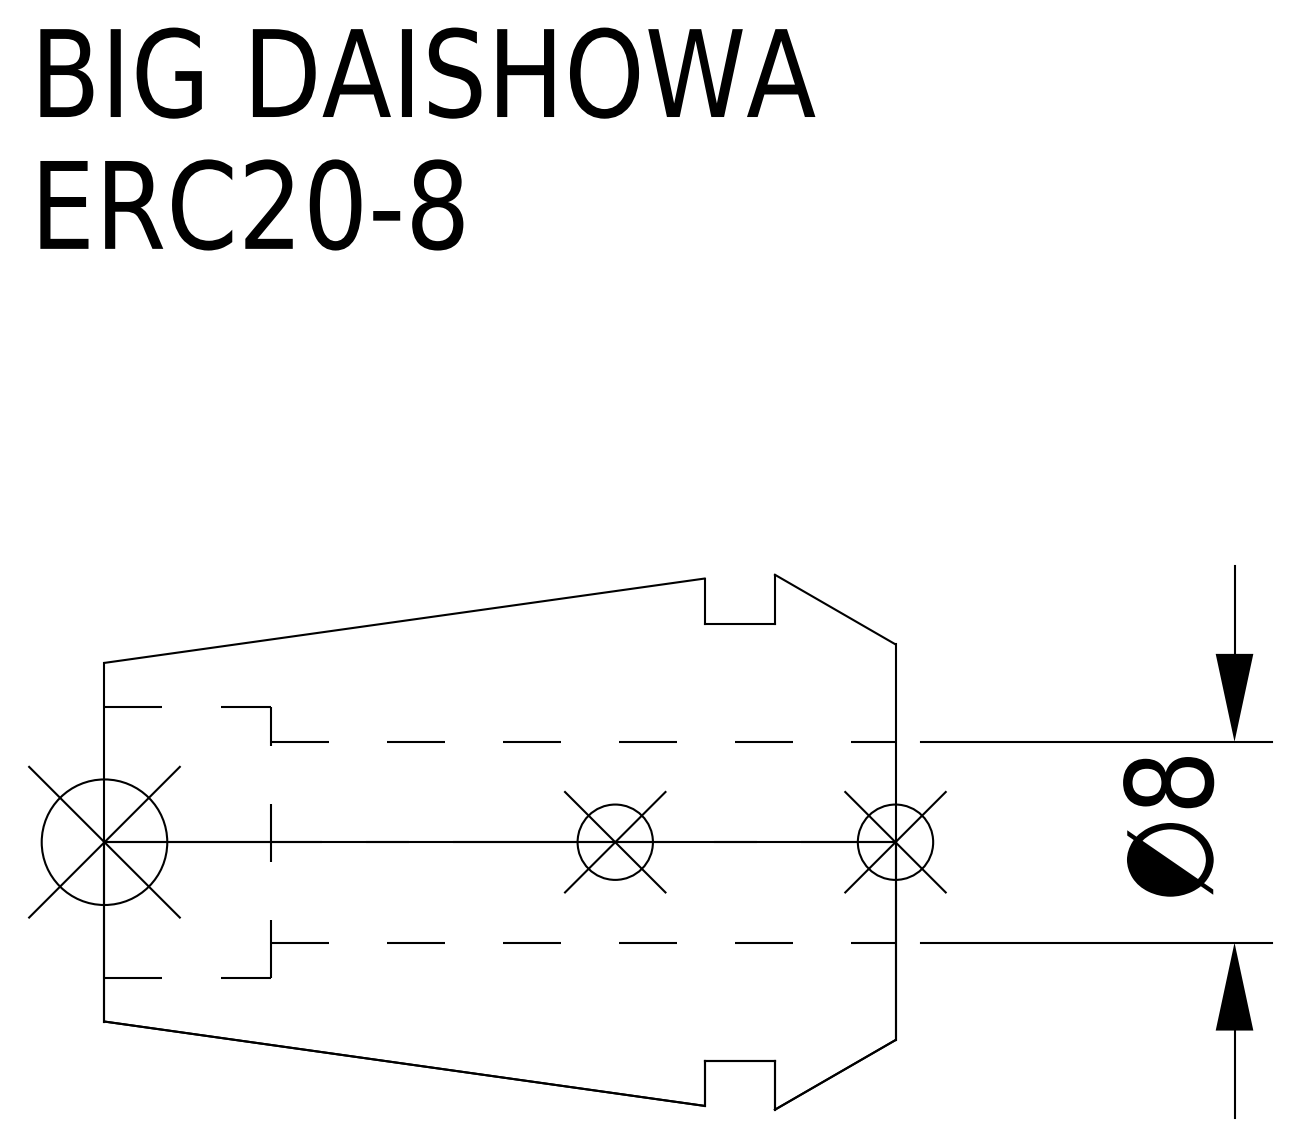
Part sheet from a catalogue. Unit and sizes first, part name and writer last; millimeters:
Units: millimetres
Overall size (bounding box): 31.5 × 21.3 × 21.3
Round holes (diameter × count): ⌀8 ×1, ⌀10.8 ×1
Round bosses / shafts (diameter × count): ⌀17.4 ×1
Main face-to-face distances: 4.8, 7.6, 2.8, 31.5, 26.7, 23.9, 24.87, 20.07, 17.27, 6.63
Volume: 6 025 mm³ · Surface area: 3 145 mm²
Bodies: 1 solid, 15 faces (5 planar, 6 cylindrical, 4 other)
Part name (STEP PRODUCT): ERC20-8
STEP written by: CREO PARAMETRIC BY PTC INC, 2016380 (AUTOMOTIVE_DESIGN)
